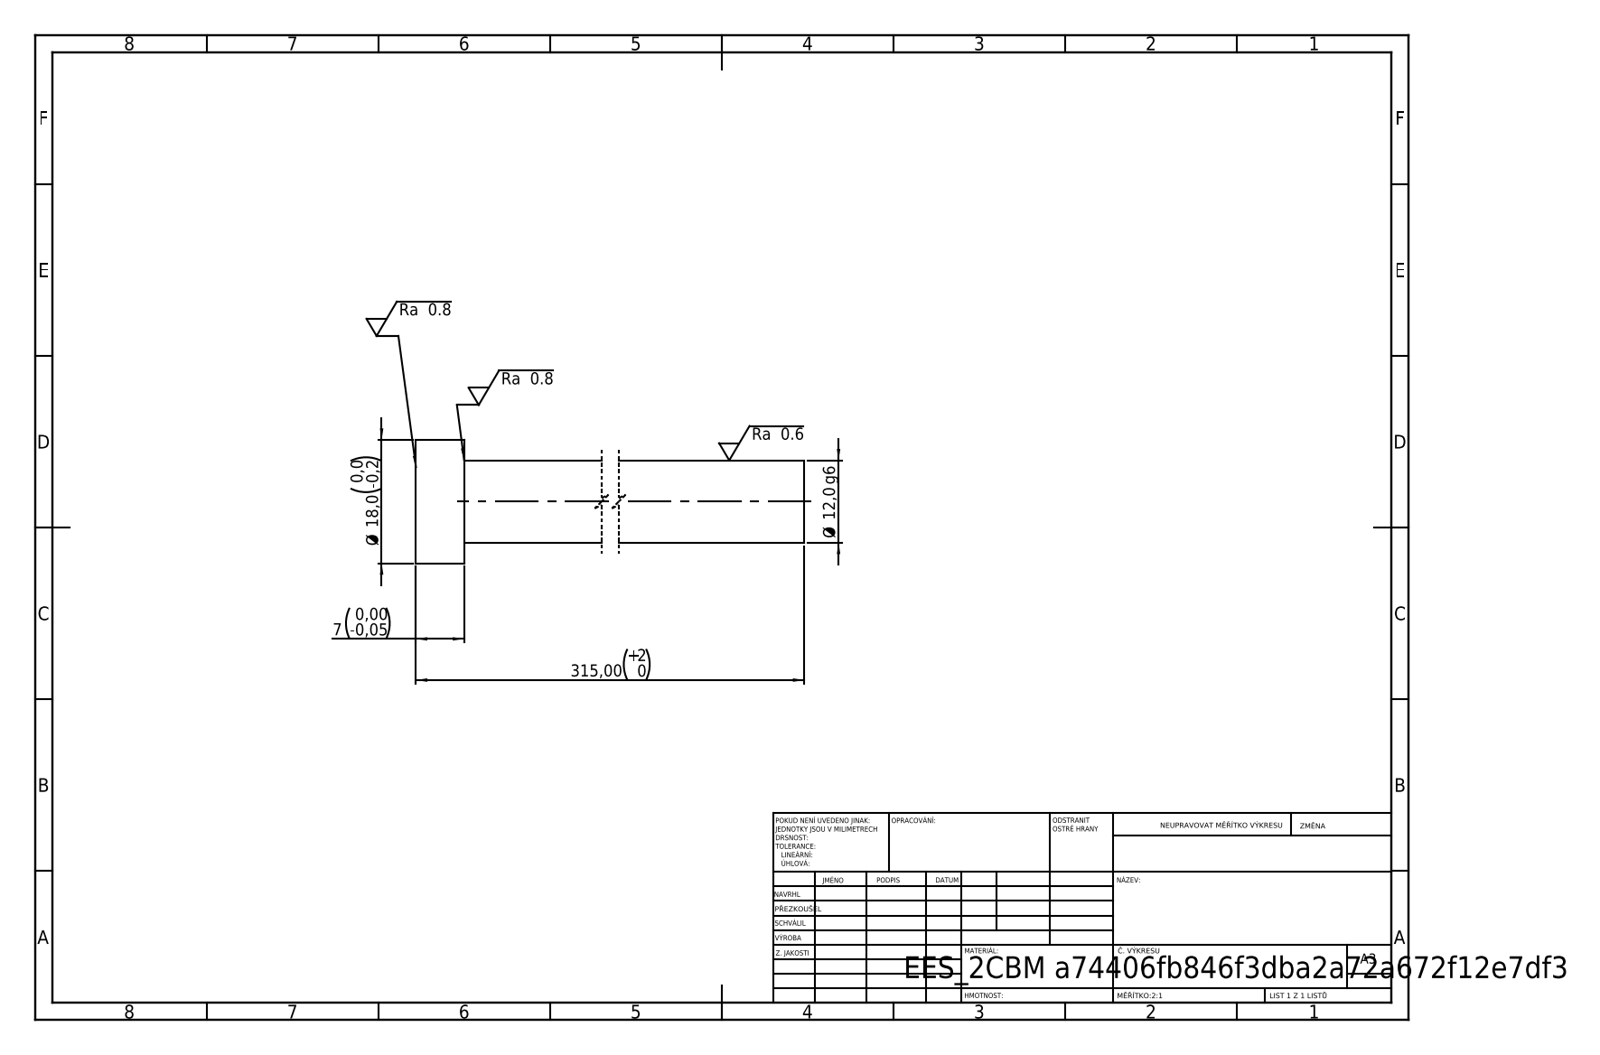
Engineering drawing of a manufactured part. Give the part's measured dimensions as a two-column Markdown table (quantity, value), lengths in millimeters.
| quantity | value |
| --- | --- |
| STEP written by | SolidWorks 2019 (CONFIG_CONTROL_DESIGN) |
| units | millimeters |
| bodies | 1 solid, 7 faces (3 planar, 4 cylindrical, 0 other) |
| overall size | 315 × 18 × 18 |
| volume | 36 615 mm³ |
| surface area | 12 516 mm² |
| round bosses / shafts (diameter × count) | 18 × 1, 12 × 1 |
| main face-to-face distances | 7, 315, 308 |
